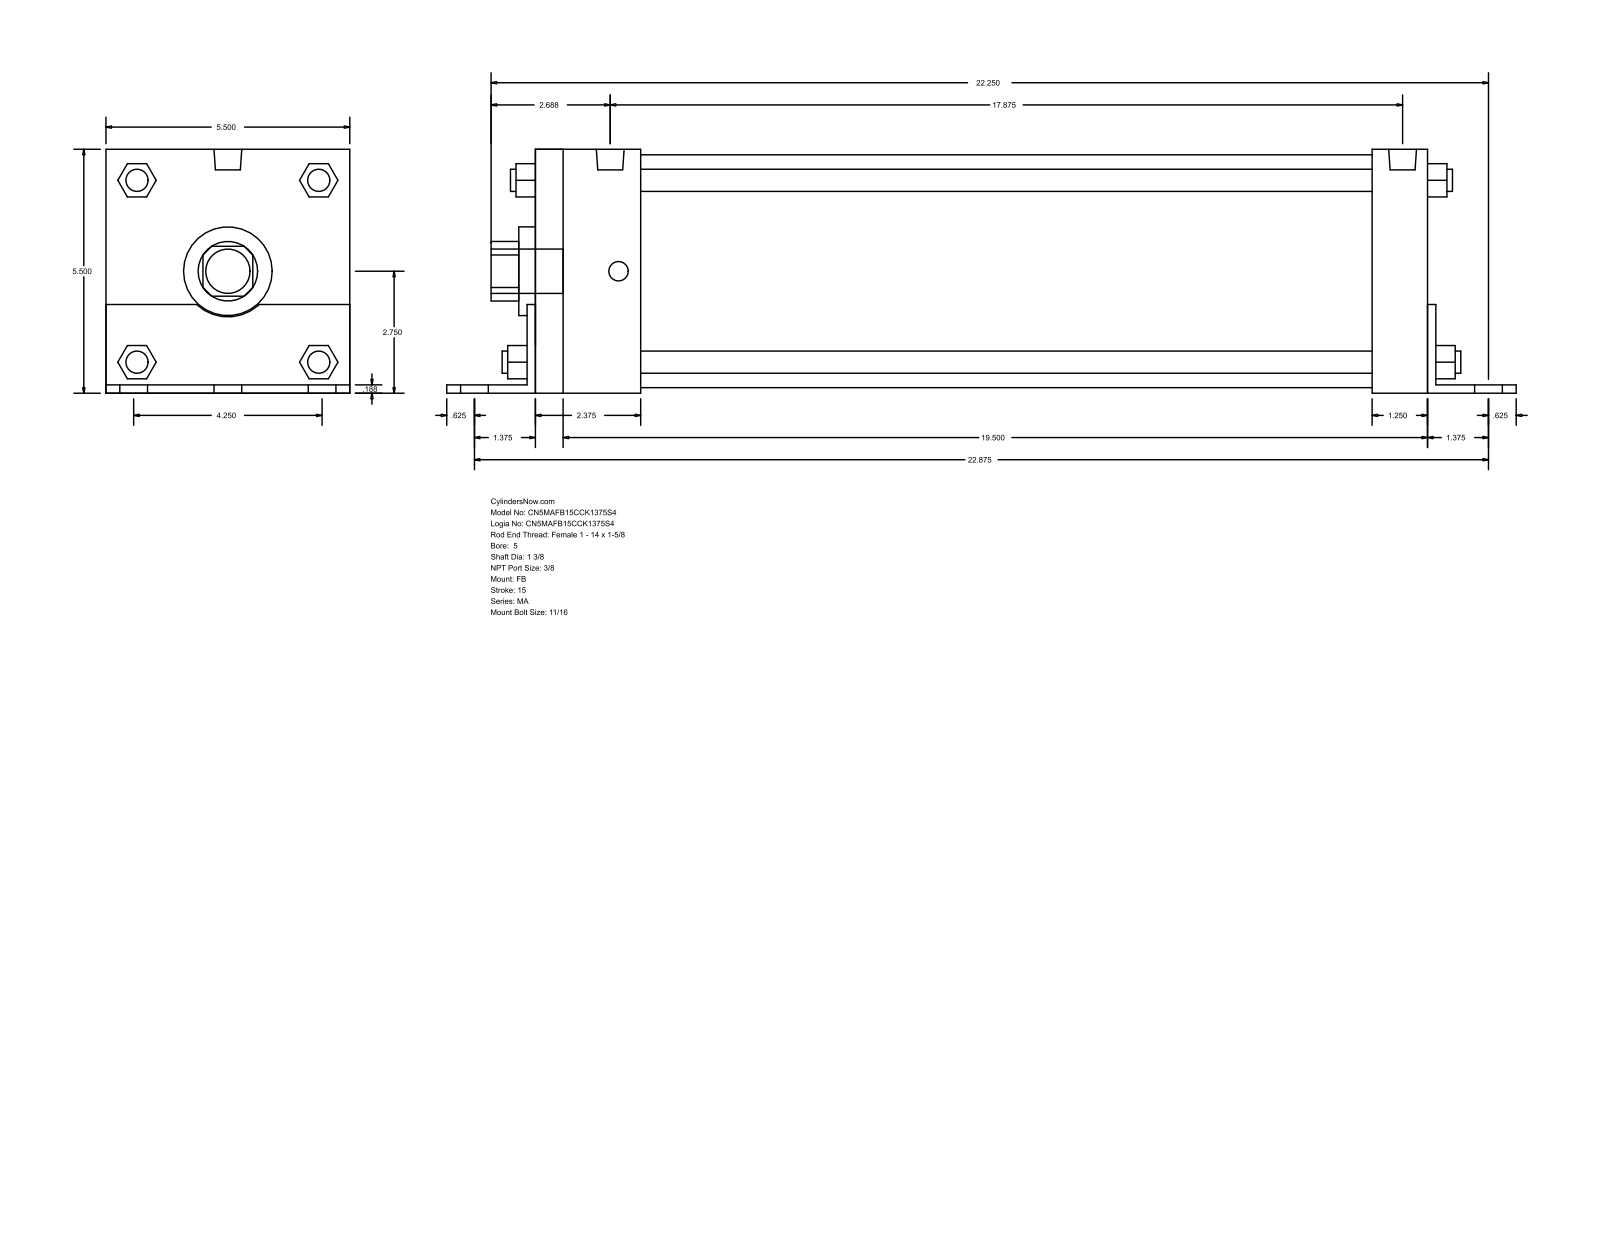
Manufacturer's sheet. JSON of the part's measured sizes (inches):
{"part_name": "MA_FB__0500_1.375", "step_written_by": "GSSL Pune (CONFIG_CONTROL_DESIGN)", "units": "inches", "bodies": {"solids": 0, "faces": 140, "planar": 105, "cylindrical": 35, "other": 0}, "overall_size": [24.125, 5.502, 5.5], "round_holes": [[1.375, 1], [2, 1], [5.25, 1]], "round_bosses_or_shafts": [[0.687, 6], [0.5, 4], [0.437, 4], [0.627, 2], [1, 1]], "partial_cylinders_radius": [[0.672, 1], [1.03, 1]], "face_to_face_distances": [5.5, 0.187, 5.502, 20.313, 0.185, 5.315, 20.125, 20.5, 1.25, 1.438]}
